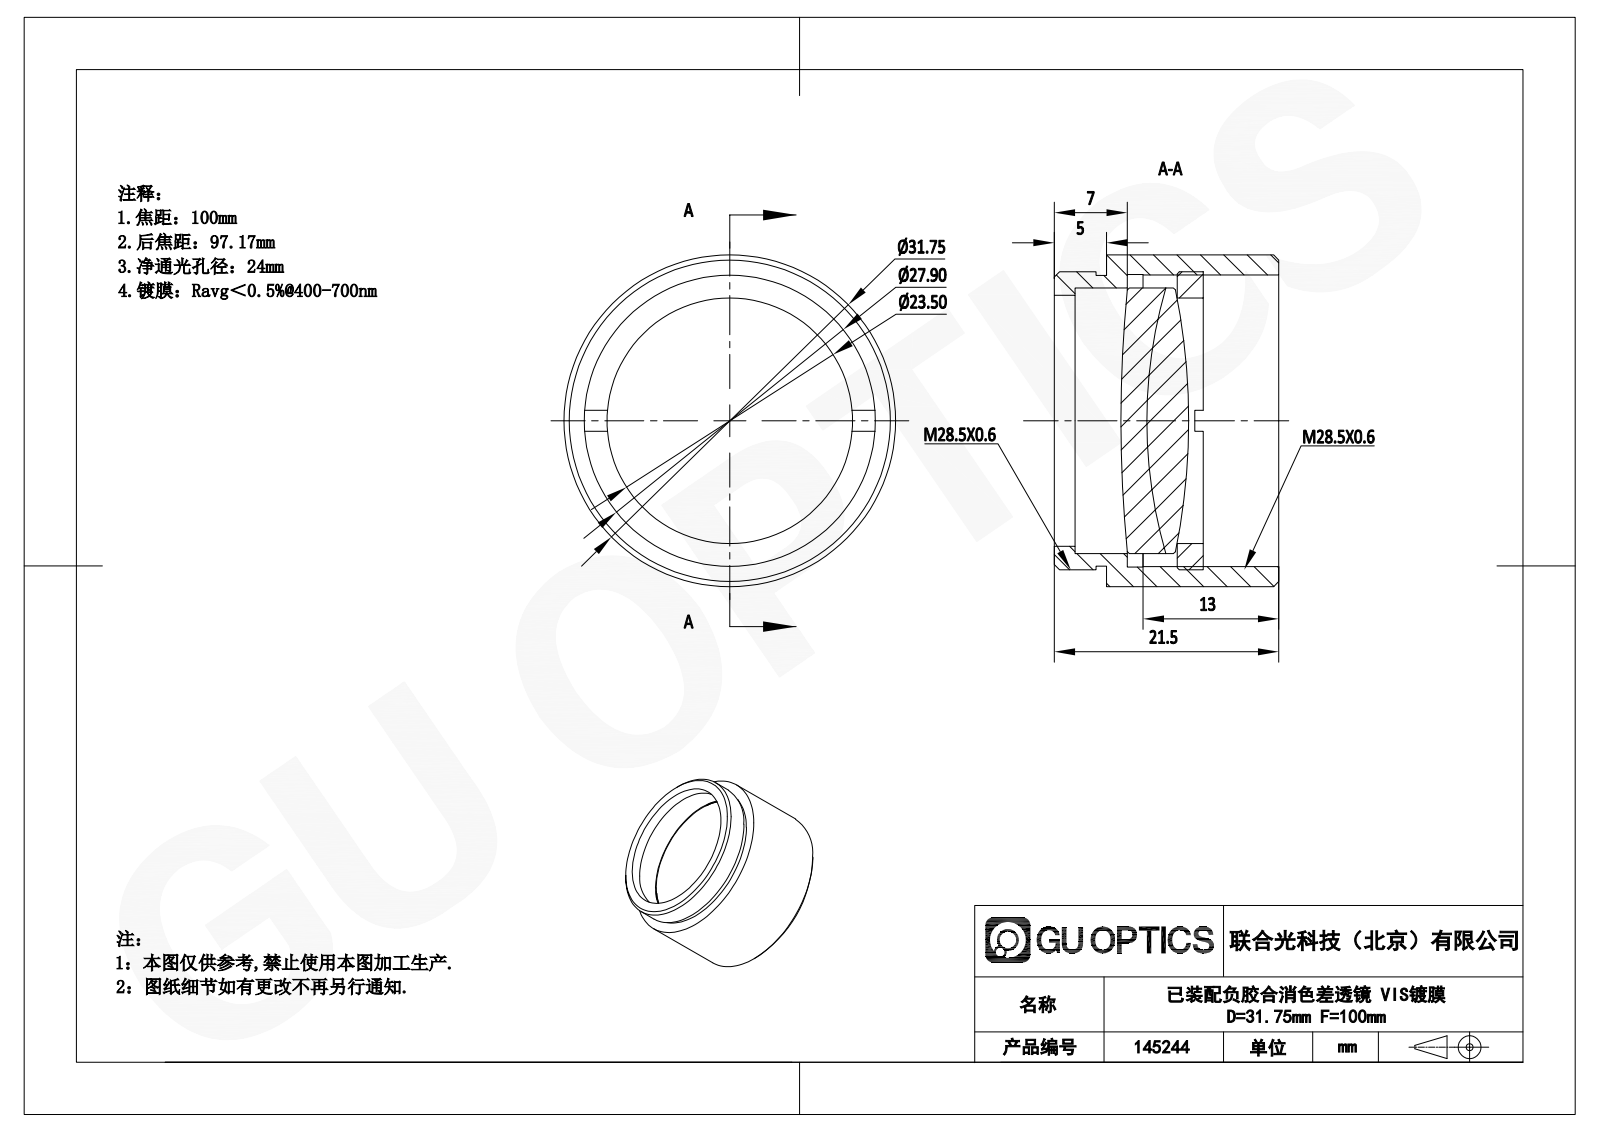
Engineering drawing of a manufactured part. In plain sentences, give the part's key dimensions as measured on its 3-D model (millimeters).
The part is named "M28.5x0.6ѹȦ; GL31-025B-100-VIS_Solidworks; APD-ML25-100-VIS". Its 3-D file was written by "SolidWorks 2022 (AUTOMOTIVE_DESIGN)". It is 4 solids with 56 faces: 16 planar, 22 cylindrical and 18 other. Overall it measures 31.76 by 31.76 by 21.5 millimeters. Its volume is 7 195 cubic millimeters and its surface area 7 819 square millimeters. Round holes: 1 of diameter 23.5, 1 of diameter 24, 1 of diameter 27.9, 1 of diameter 28. Round bosses or shafts: 1 of diameter 31.76, 1 of diameter 28.5, 1 of diameter 27.8, 1 of diameter 25.4. The main face-to-face distances are 2, 5, 2.5, 6.76, 9.26, 11.76, 14.26, 21.5, 16.5, 9.74.
